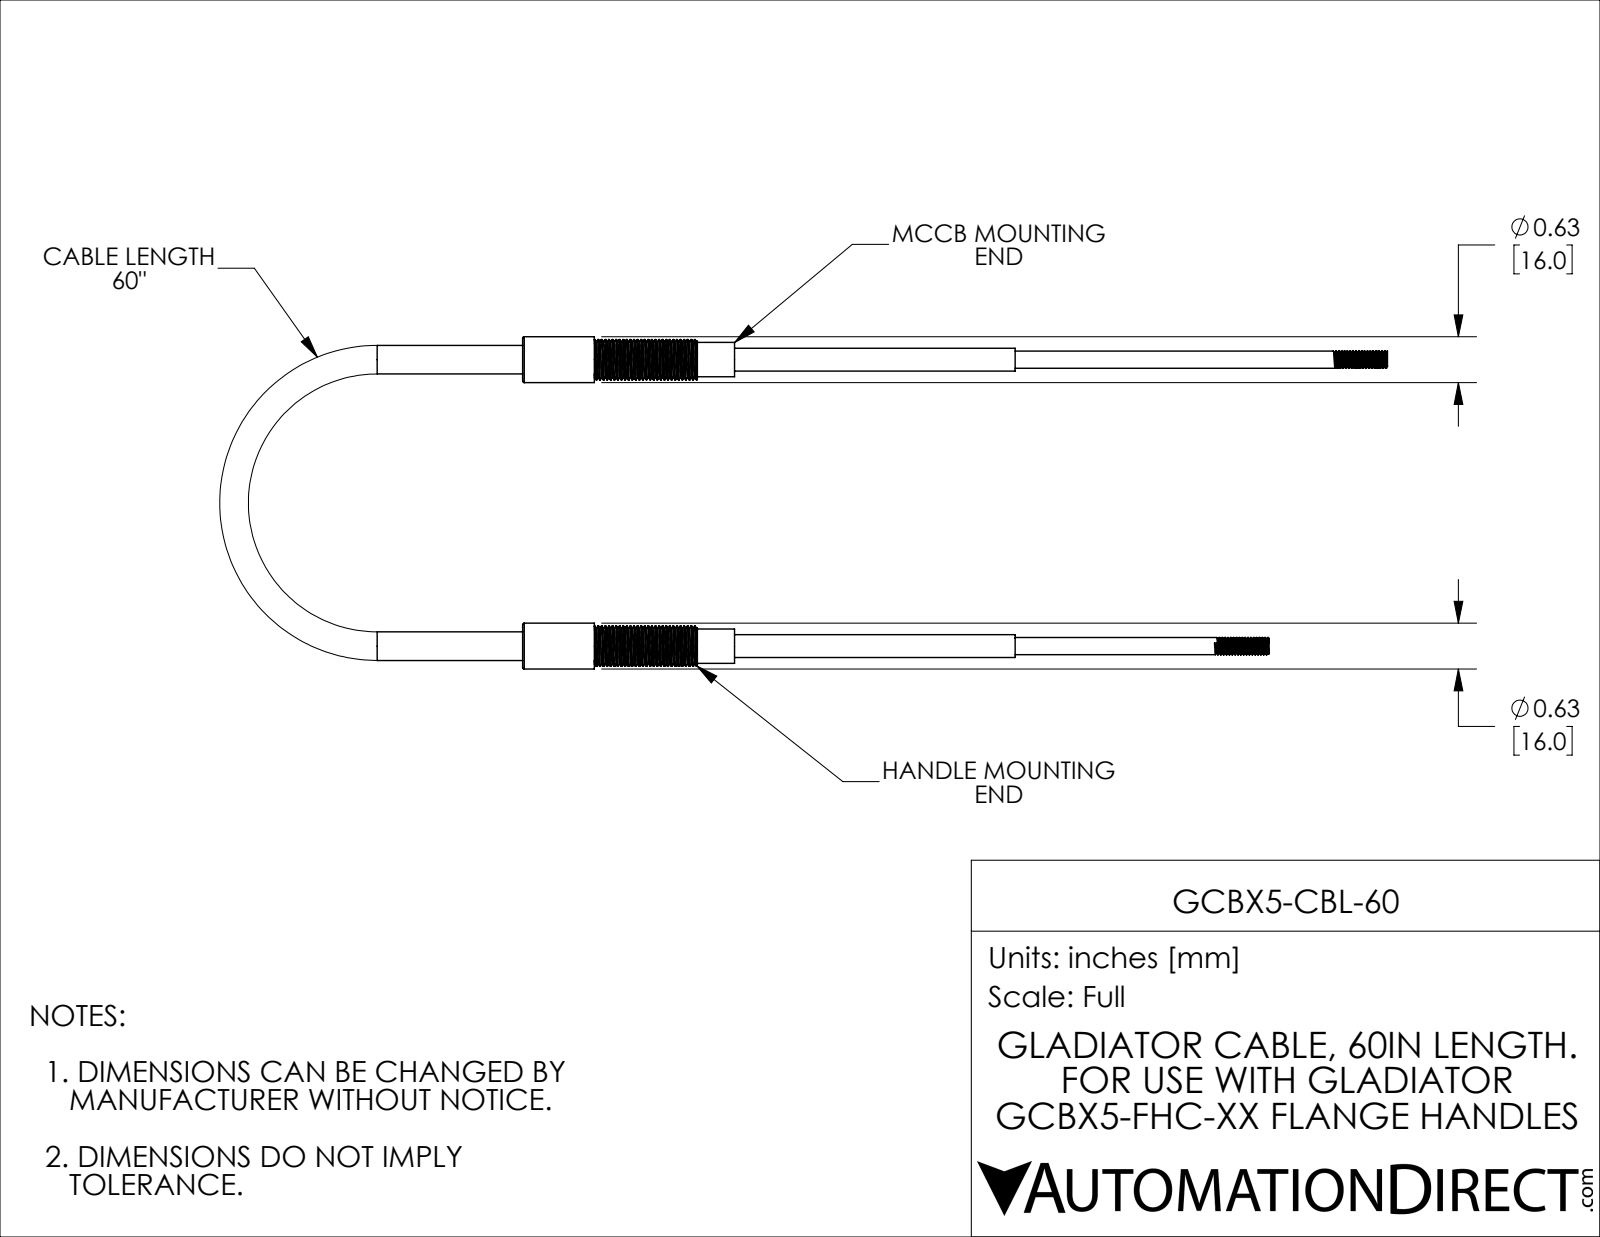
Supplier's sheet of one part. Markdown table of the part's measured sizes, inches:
| quantity | value |
| --- | --- |
| part name | GCBX5-CBL-60; GCBX5-CBL-60_1; GCBX5-CBL-60_2 |
| STEP written by | SolidWorks 2021 (CONFIG_CONTROL_DESIGN) |
| units | inches |
| bodies | 8 solids, 300 faces (24 planar, 218 cylindrical, 58 other) |
| overall size | 13.89 × 4.567 × 0.63 |
| volume | 1.901 in³ |
| surface area | 50.13 in² |
| round holes (diameter × count) | 0.394 × 2 |
| round bosses / shafts (diameter × count) | 0.63 × 2, 0.551 × 2, 0.472 × 2, 0.315 × 2, 0.236 × 2 |
| main face-to-face distances | 2, 2.984, 0.984, 8.772, 6.772, 5.787, 4.913, 2.913, 1.929, 3.858 |
| hole center spacings | 3.937 |
